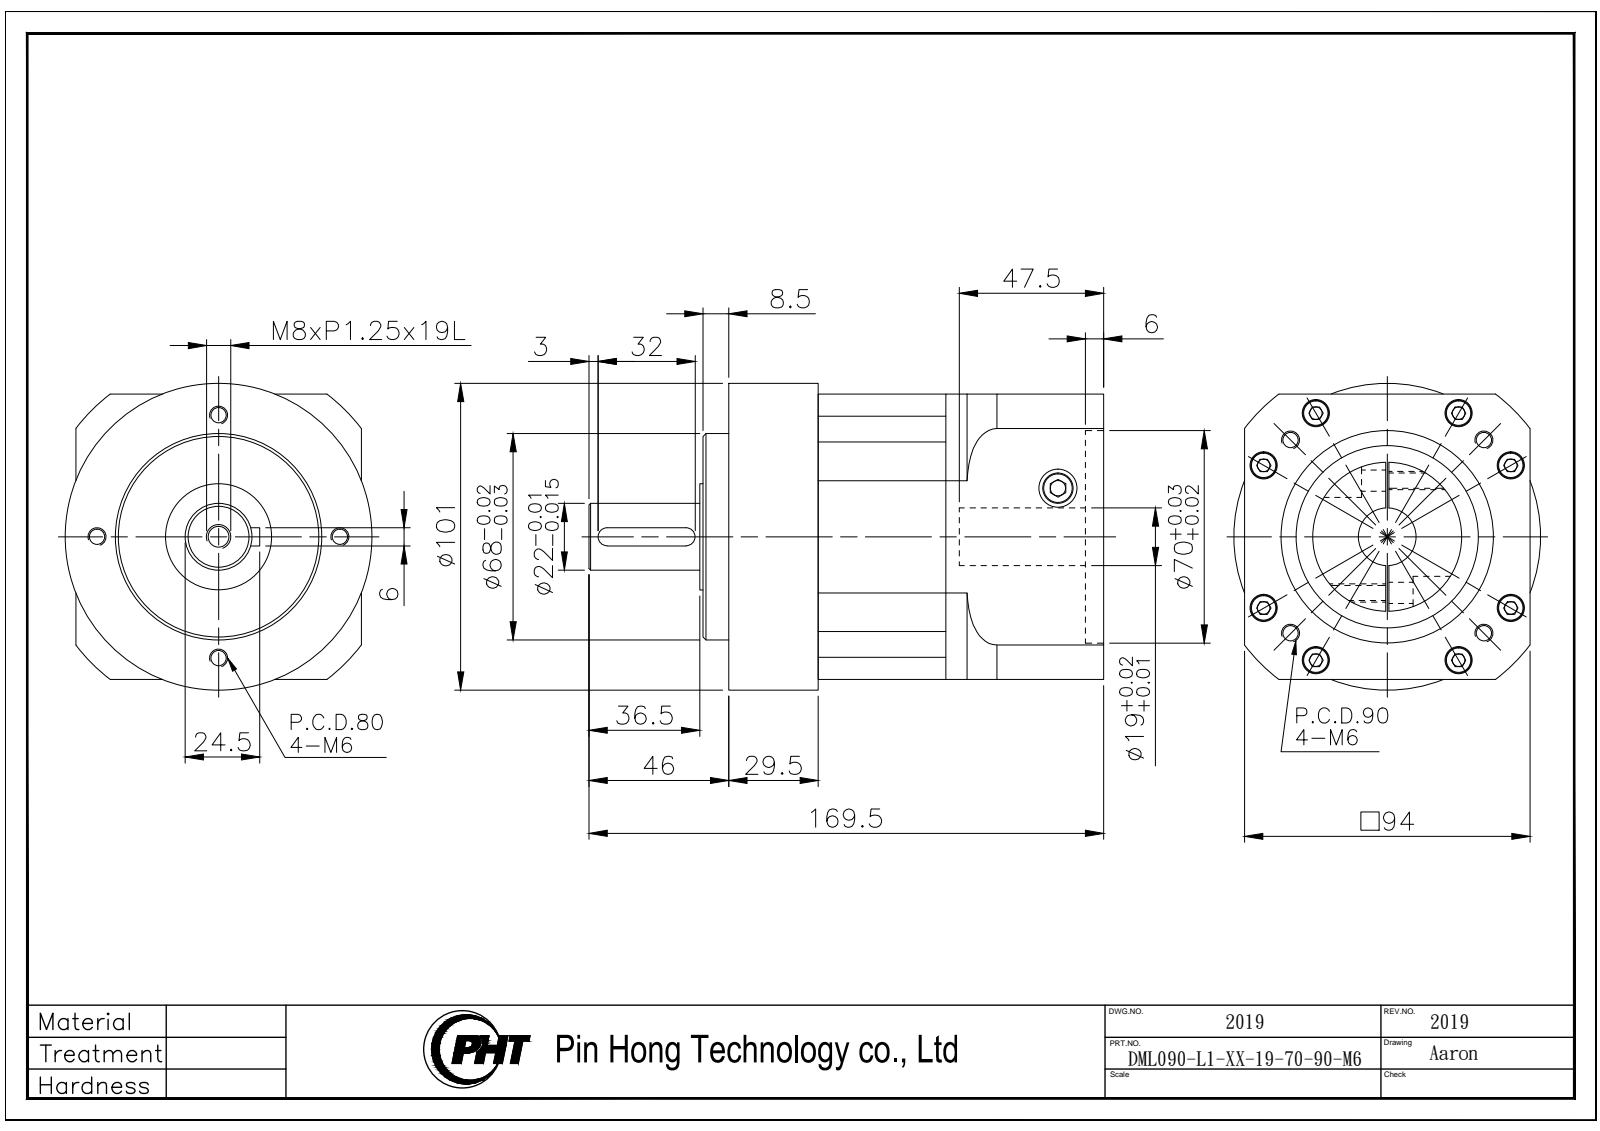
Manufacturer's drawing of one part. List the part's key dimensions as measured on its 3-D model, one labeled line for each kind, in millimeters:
Part name (STEP PRODUCT): DML090-L1-XX-19-70-90-M6_2019
STEP written by: SolidWorks 2016 (AUTOMOTIVE_DESIGN)
Units: millimetres
Bodies: 3 solids, 261 faces (108 planar, 113 cylindrical, 40 other)
Overall size (bounding box): 169.5 × 101 × 101
Volume: 928 741 mm³ · Surface area: 128 131 mm²
Round holes (diameter × count): ⌀5 ×8, ⌀5.2 ×8, ⌀9 ×8, ⌀12.7 ×2, ⌀6.8 ×1, ⌀19 ×1, ⌀60 ×1, ⌀70 ×1
Round bosses / shafts (diameter × count): ⌀8.5 ×8, ⌀101 ×1, ⌀68 ×1, ⌀49 ×1, ⌀35 ×1, ⌀22 ×1
Partial cylindrical surfaces — rounded edges, fillets, slot ends (radius × count): R6 ×4, R3 ×2, R59 ×1
Main face-to-face distances: 42, 94, 71.5, 29.5, 52, 123.5, 46, 132, 80, 38
Hole centre spacings: 47, 12.17, 23.51, 32.85, 43.92, 56.03, 66.46, 73
